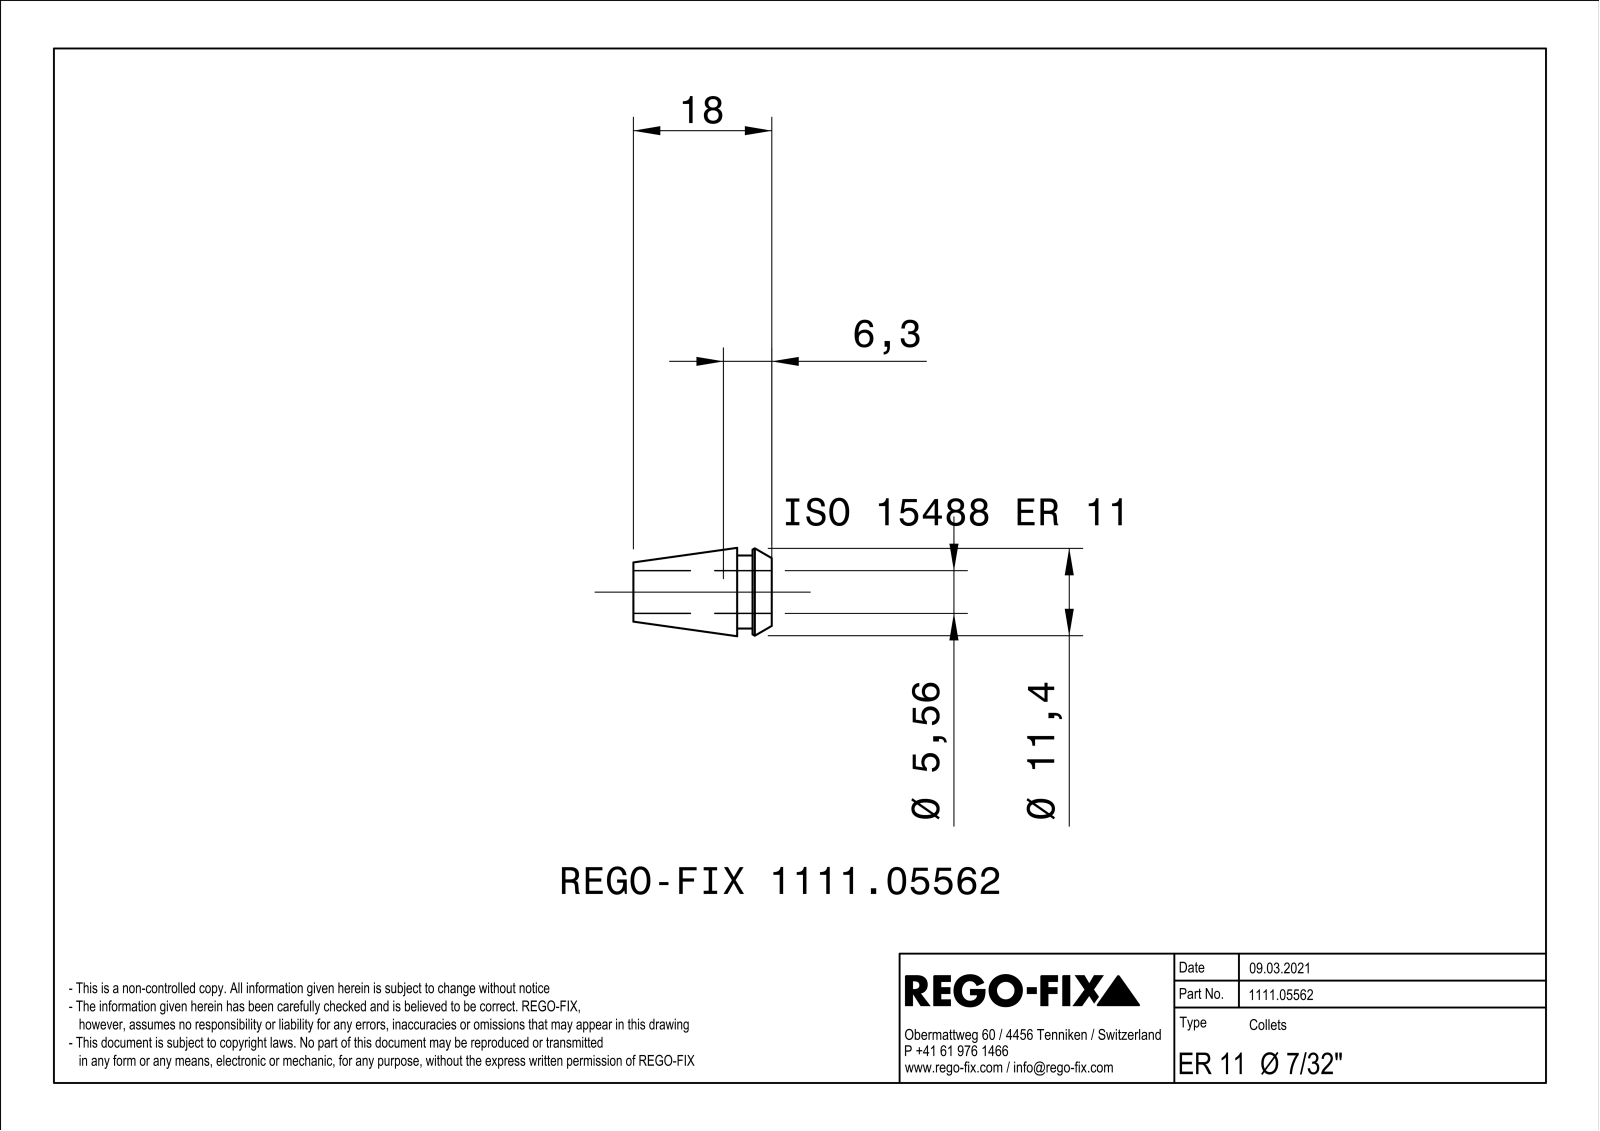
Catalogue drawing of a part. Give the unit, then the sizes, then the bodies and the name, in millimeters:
Units: millimetres
Overall size (bounding box): 18 × 11.5 × 11.49
Round holes (diameter × count): ⌀5.56 ×1
Round bosses / shafts (diameter × count): ⌀11.5 ×1, ⌀9.5 ×1
Partial cylindrical surfaces — rounded edges, fillets, slot ends (radius × count): R25 ×12
Main face-to-face distances: 0.45, 0.46, 0.44, 2.5, 4.5, 2, 18, 15.5, 13.5, 4
Volume: 740 mm³ · Surface area: 1 558 mm²
Bodies: 1 solid, 157 faces (66 planar, 37 cylindrical, 54 other)
Part name (STEP PRODUCT): NOCUT
STEP written by: SIEMENS PLM Software Solid Edge ST10 (AUTOMOTIVE_DESIGN)
